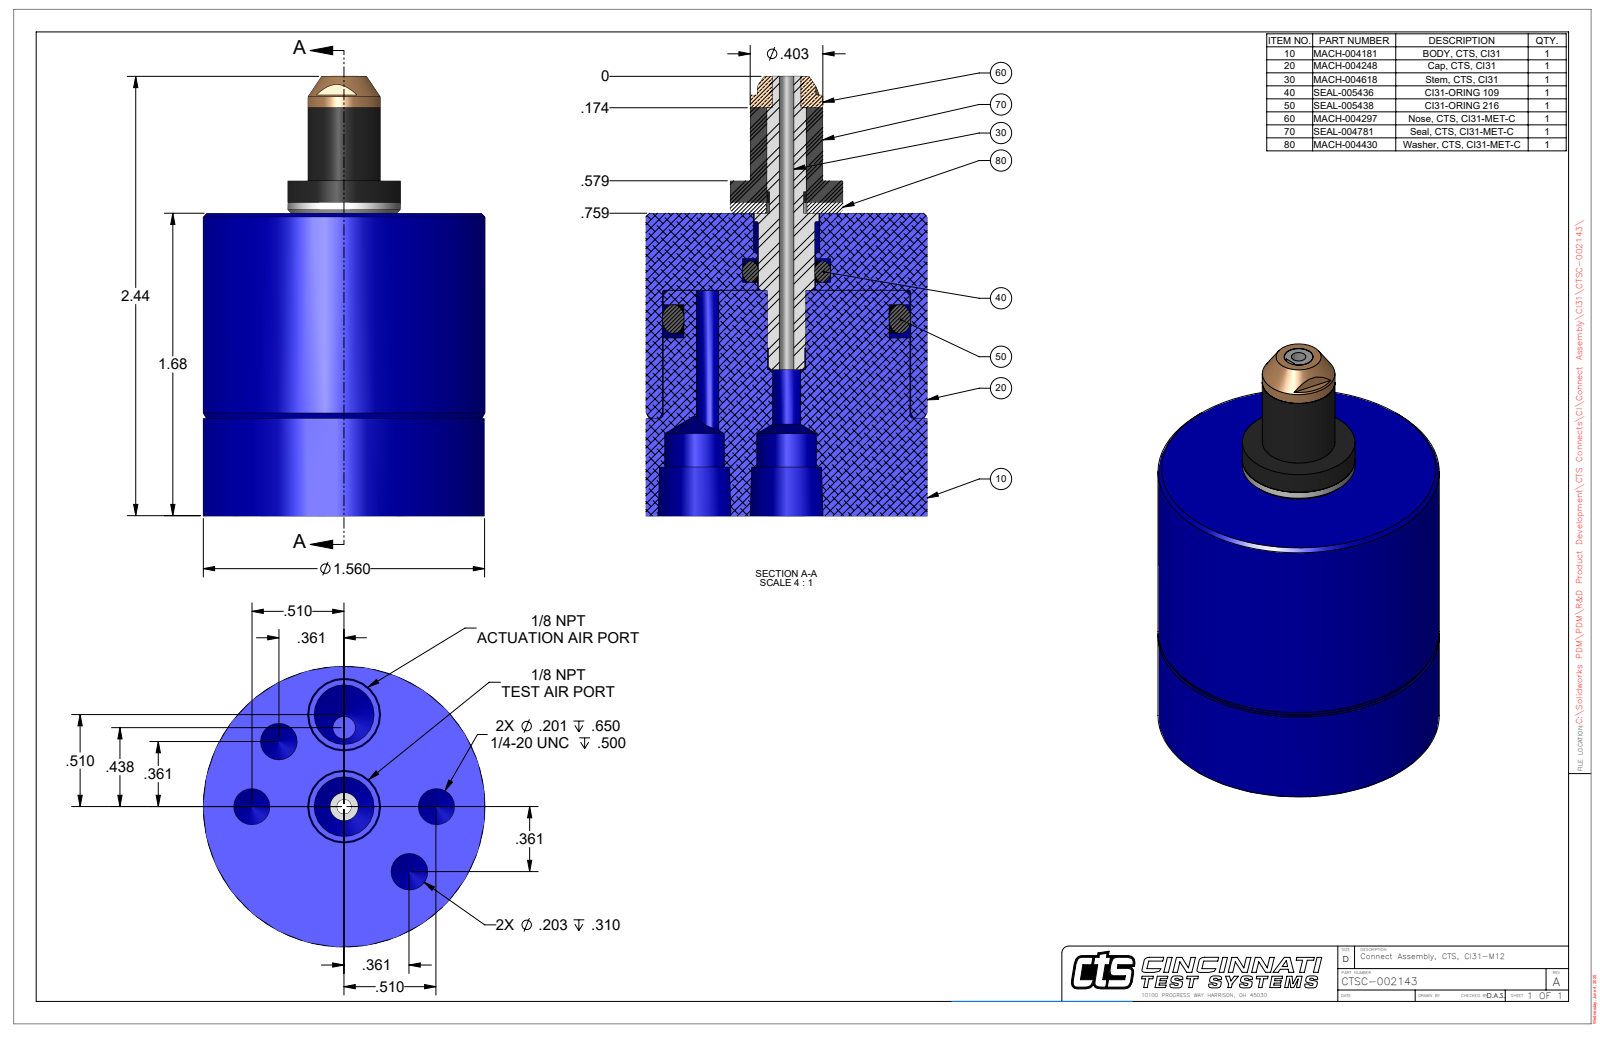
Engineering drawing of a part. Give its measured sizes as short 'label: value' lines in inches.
name: CTSC-002143
written by: SolidWorks 2023 (AUTOMOTIVE_DESIGN)
unit: in
bodies: 1 solid, 87 faces (22 planar, 35 cylindrical, 30 other)
size: 2.437 × 1.56 × 1.56
volume: 3.132 in³; area: 18.62 in²
holes: 2× ⌀0.201, 2× ⌀0.203, 2× ⌀0.332, 1× ⌀0.081, 1× ⌀0.125, 1× ⌀0.156, 1× ⌀0.368, 1× ⌀1.377
bosses: 1× ⌀1.56, 1× ⌀1.365, 1× ⌀0.625, 1× ⌀0.403, 1× ⌀0.357
rounds: 1× R0.079
face distances: 1.677, 1.857, 0.18, 0.542, 1.135, 1.315, 0.812, 0.27, 0.865, 1.045
hole spacings: 0.51, 0.39, 0.942, 0.672, 0.721, 0.072, 0.369, 0.437
